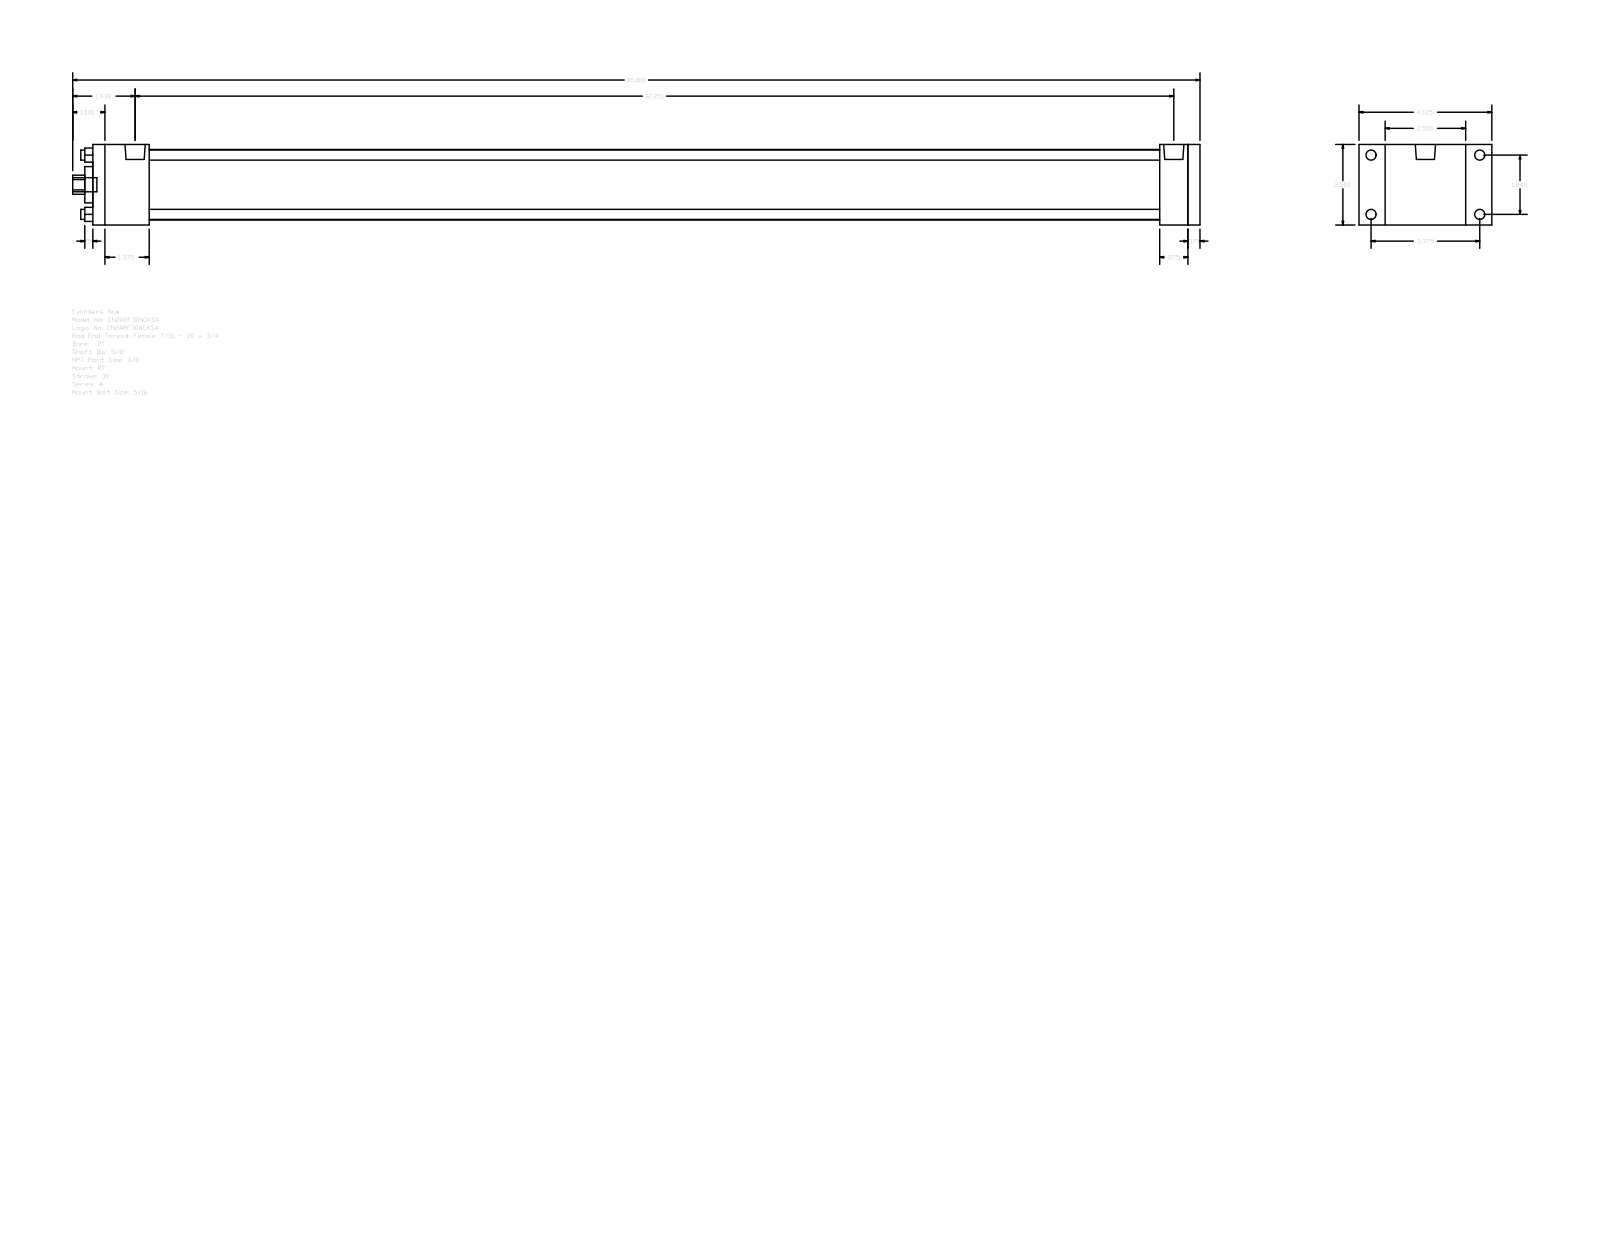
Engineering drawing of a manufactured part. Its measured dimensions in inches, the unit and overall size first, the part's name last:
Units: inches
Overall size (bounding box): 35 × 4.125 × 2.5
Round holes (diameter × count): ⌀0.313 ×4, ⌀0.625 ×1, ⌀1.125 ×1, ⌀2.19 ×1
Round bosses / shafts (diameter × count): ⌀0.313 ×4, ⌀0.219 ×4, ⌀0.627 ×2, ⌀0.437 ×1
Partial cylindrical surfaces — rounded edges, fillets, slot ends (radius × count): R0.297 ×1
Main face-to-face distances: 2.5, 34.375, 0.375, 34, 1.75, 32.25, 32.625, 33.125, 31.375, 0.875
Hole centre spacings: 1.301, 1.84, 2.602
Bodies: 0 solids, 92 faces (64 planar, 28 cylindrical, 0 other)
Part name (STEP PRODUCT): A_RF__0200_0.625
STEP written by: GSSL Pune (CONFIG_CONTROL_DESIGN)
